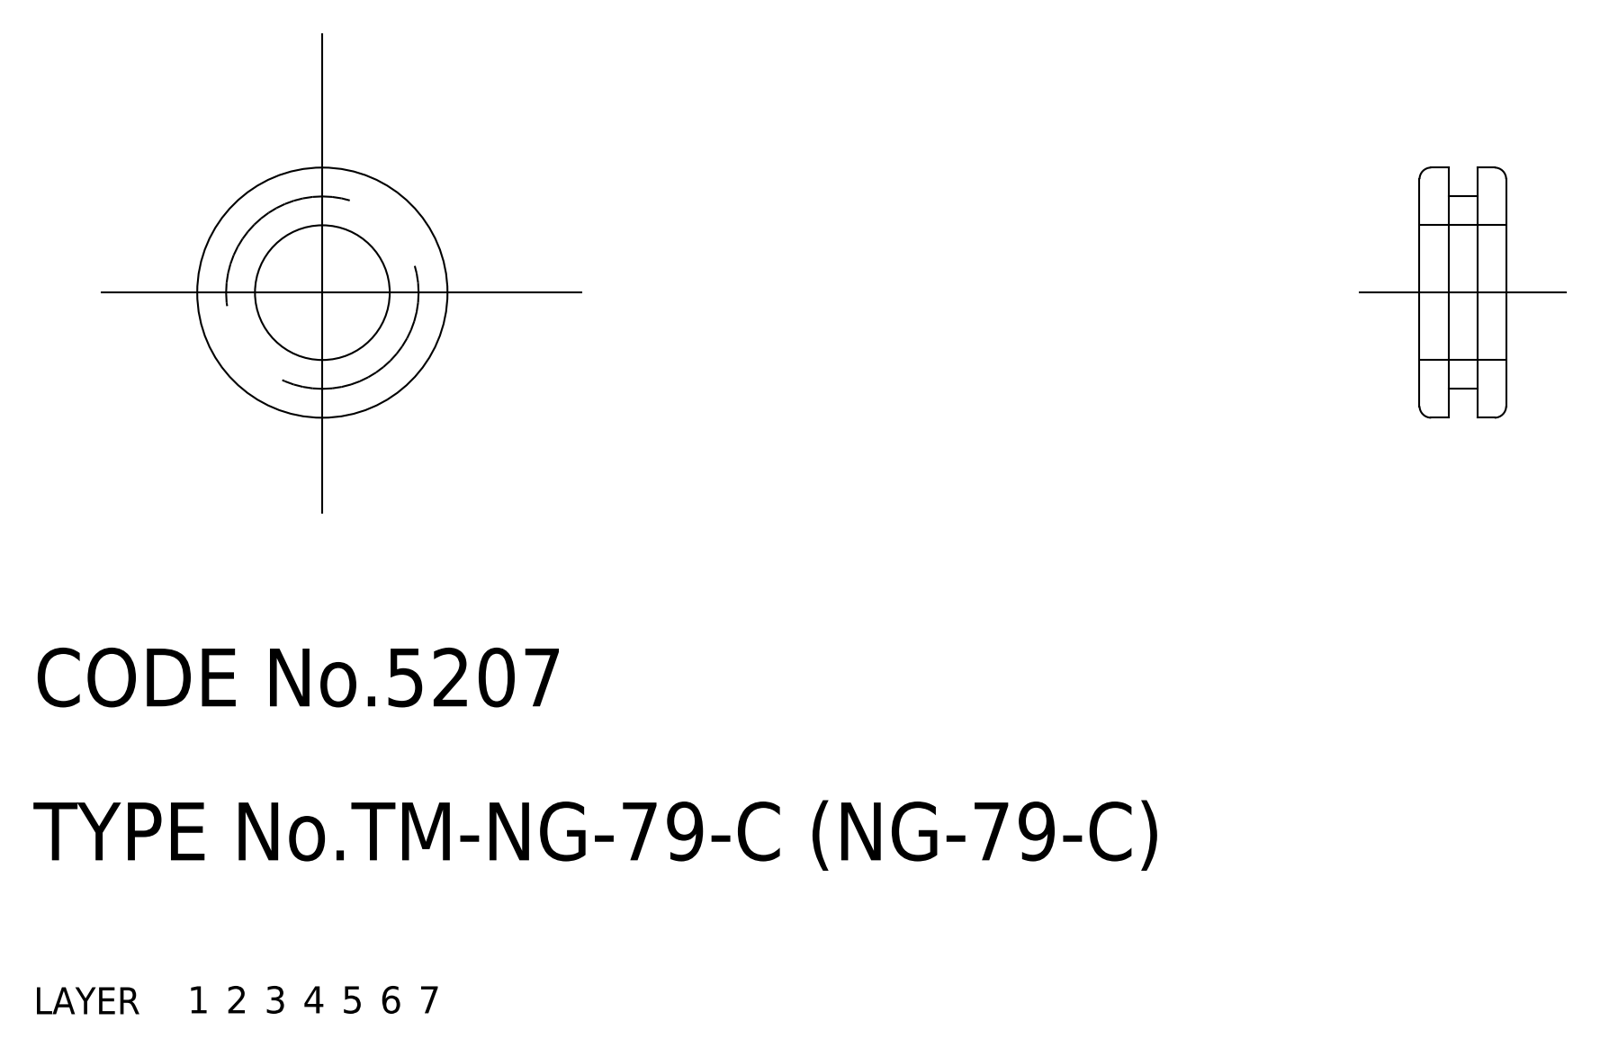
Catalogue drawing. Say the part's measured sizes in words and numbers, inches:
The part is named "grommet". Its 3-D file was written by "CADfix (AUTOMOTIVE_DESIGN)". It is 1 solid with 16 faces: 0 planar, 0 cylindrical and 16 other. Overall it measures 0.512 by 0.512 by 0.177 inches. Its volume is 0.021 cubic inches and its surface area 0.843 square inches.
